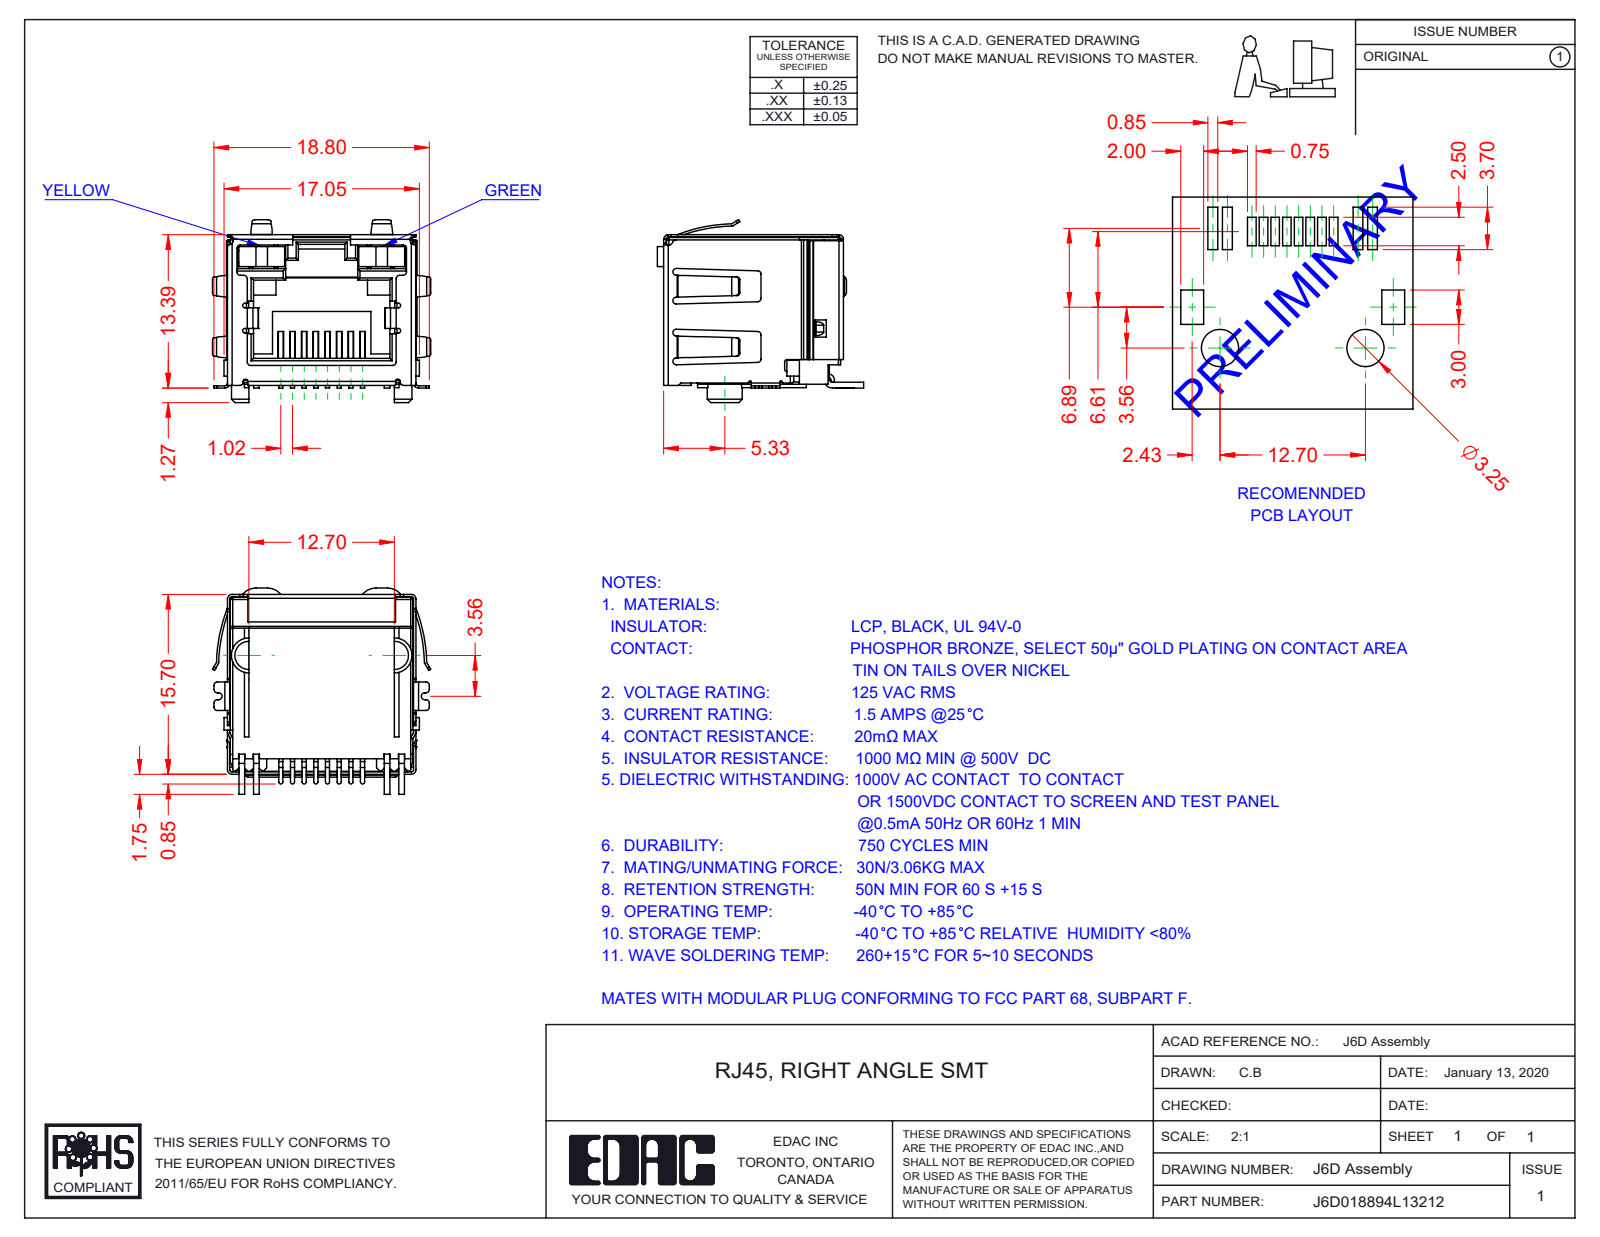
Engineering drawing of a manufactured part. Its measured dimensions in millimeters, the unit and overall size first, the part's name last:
Units: millimetres
Overall size (bounding box): 19.06 × 18 × 15.95
Partial cylindrical surfaces — rounded edges, fillets, slot ends (radius × count): R0.3 ×55, R0.2 ×40, R0.4 ×19, R0.25 ×16, R0.1 ×12, R0.15 ×8, R0.18 ×8, R0.5 ×6
Main face-to-face distances: 16, 16.2, 16.25, 2.25, 1, 15.95, 12.8, 0.45, 13.05, 10.6
Volume: 1 790 mm³ · Surface area: 4 796 mm²
Bodies: 12 solids, 1028 faces (701 planar, 282 cylindrical, 45 other)
Part name (STEP PRODUCT): 6D Contacts; 6D LED RH_3-Green; J6D018894L13212; 6D Shield_LED - EMI (+2 more)
STEP written by: SolidWorks 2016 (CONFIG_CONTROL_DESIGN)
